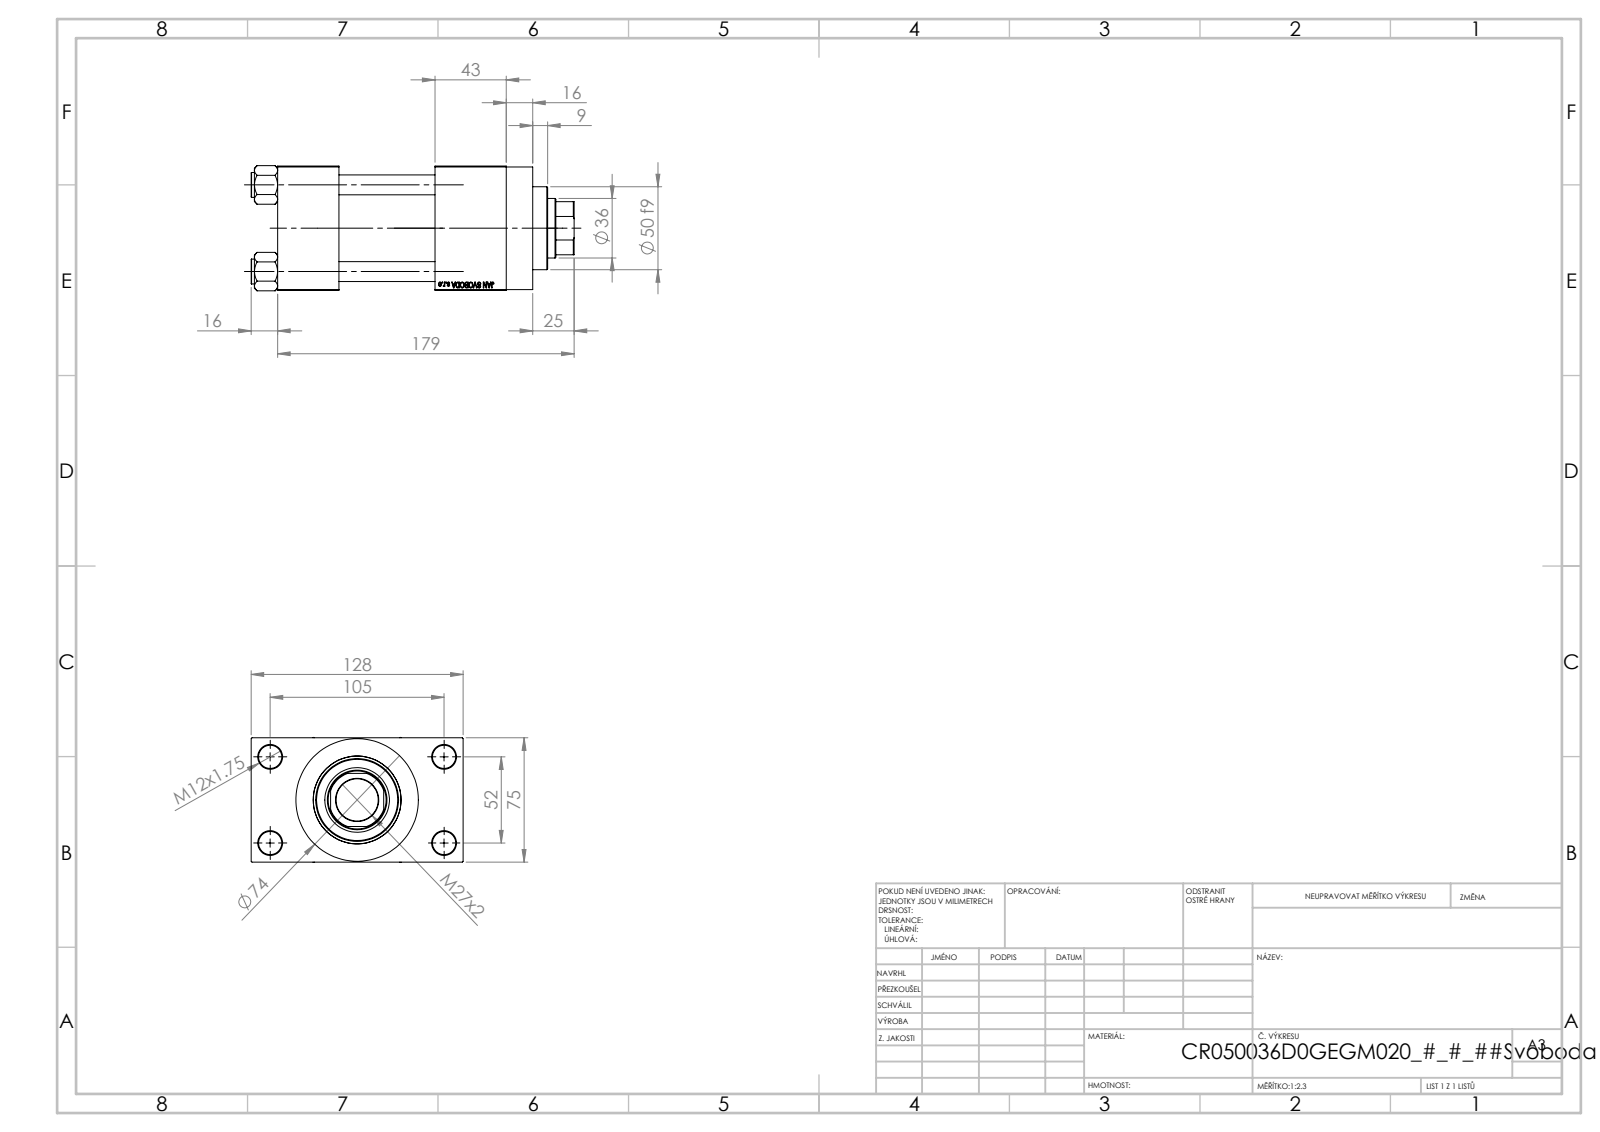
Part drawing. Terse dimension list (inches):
name: V215_VC_A; V215CR_D_TYCINKA; V215CR_VCP_D; V215CR_D_Body (+1 more)
written by: SolidWorks 2019 (CONFIG_CONTROL_DESIGN)
unit: in
bodies: 11 solids, 1104 faces (497 planar, 89 cylindrical, 518 other)
size: 7.677 × 5.039 × 2.974
volume: 50.43 in³; area: 269.4 in²
holes: 4× ⌀0.472, 4× ⌀0.551, 2× ⌀0.276, 2× ⌀0.825, 2× ⌀1.181, 1× ⌀1.004, 1× ⌀1.417, 1× ⌀1.535, 1× ⌀1.614, 1× ⌀2.087
bosses: 4× ⌀0.591, 1× ⌀2.913, 1× ⌀2.205, 1× ⌀1.969
rounds: 1× R0.689
face distances: 2.953, 2.283, 1.457, 3.74, 1.043, 3.996, 1.693, 5.433, 3.976, 0.63
hole spacings: 1.037, 1.456, 2.059, 2.3, 2.307, 3.096, 3.715, 2.047
